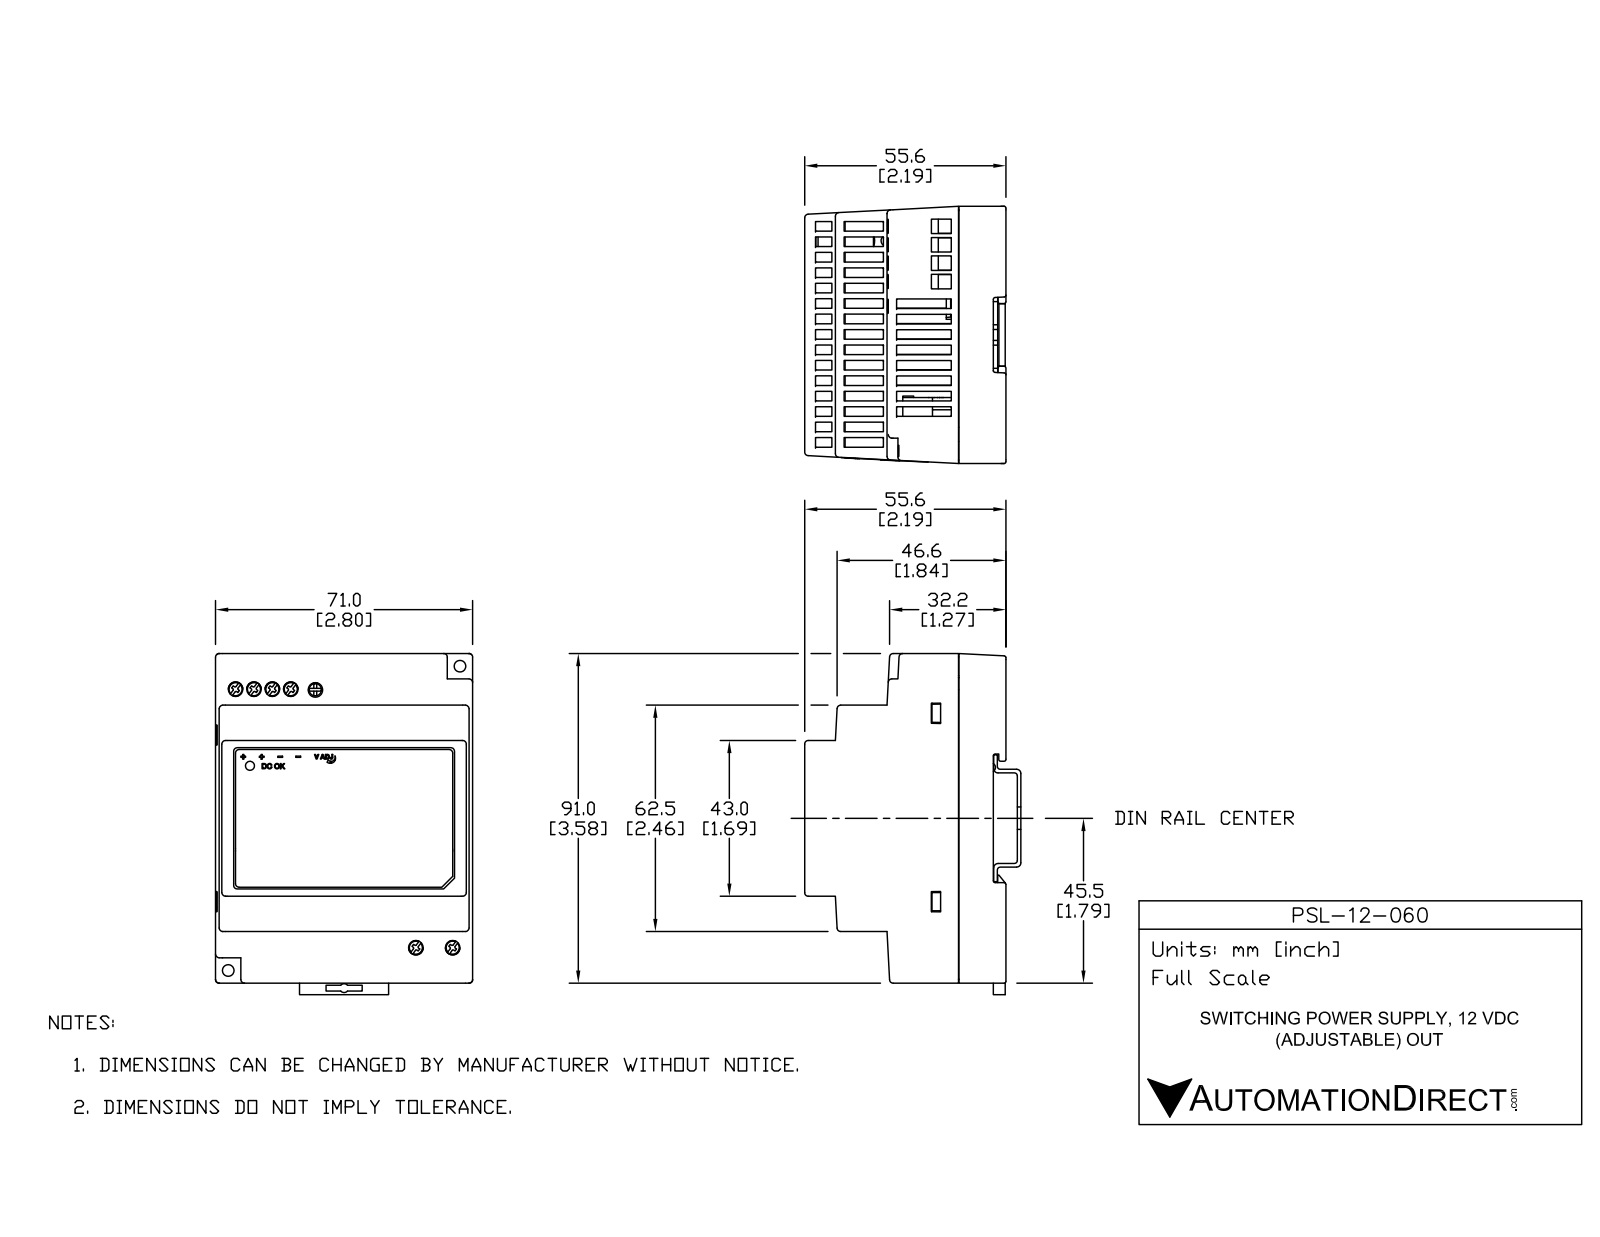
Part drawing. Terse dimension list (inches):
name: PSL-12-060
written by: SolidWorks 2017 (AUTOMOTIVE_DESIGN)
unit: in
bodies: 4 solids, 947 faces (656 planar, 189 cylindrical, 102 other)
size: 3.707 × 2.795 × 2.209
volume: 3.264 in³; area: 91.9 in²
holes: 7× ⌀0.157, 2× ⌀0.098, 2× ⌀0.126, 1× ⌀0.138
bosses: 1× ⌀0.156
rounds: 81× R0.02, 47× R0.039, 6× R0.008, 2× R0.04, 2× R0.059, 2× R0.128, 2× R0.142, 1× R0.048
face distances: 0.079, 0.087, 0.079, 1.886, 1.972, 0.541, 2.043, 1.957, 0.071, 0.561
hole spacings: 0.2, 0.4, 2.055, 3.315, 3.425, 0.268, 0.277, 0.349
